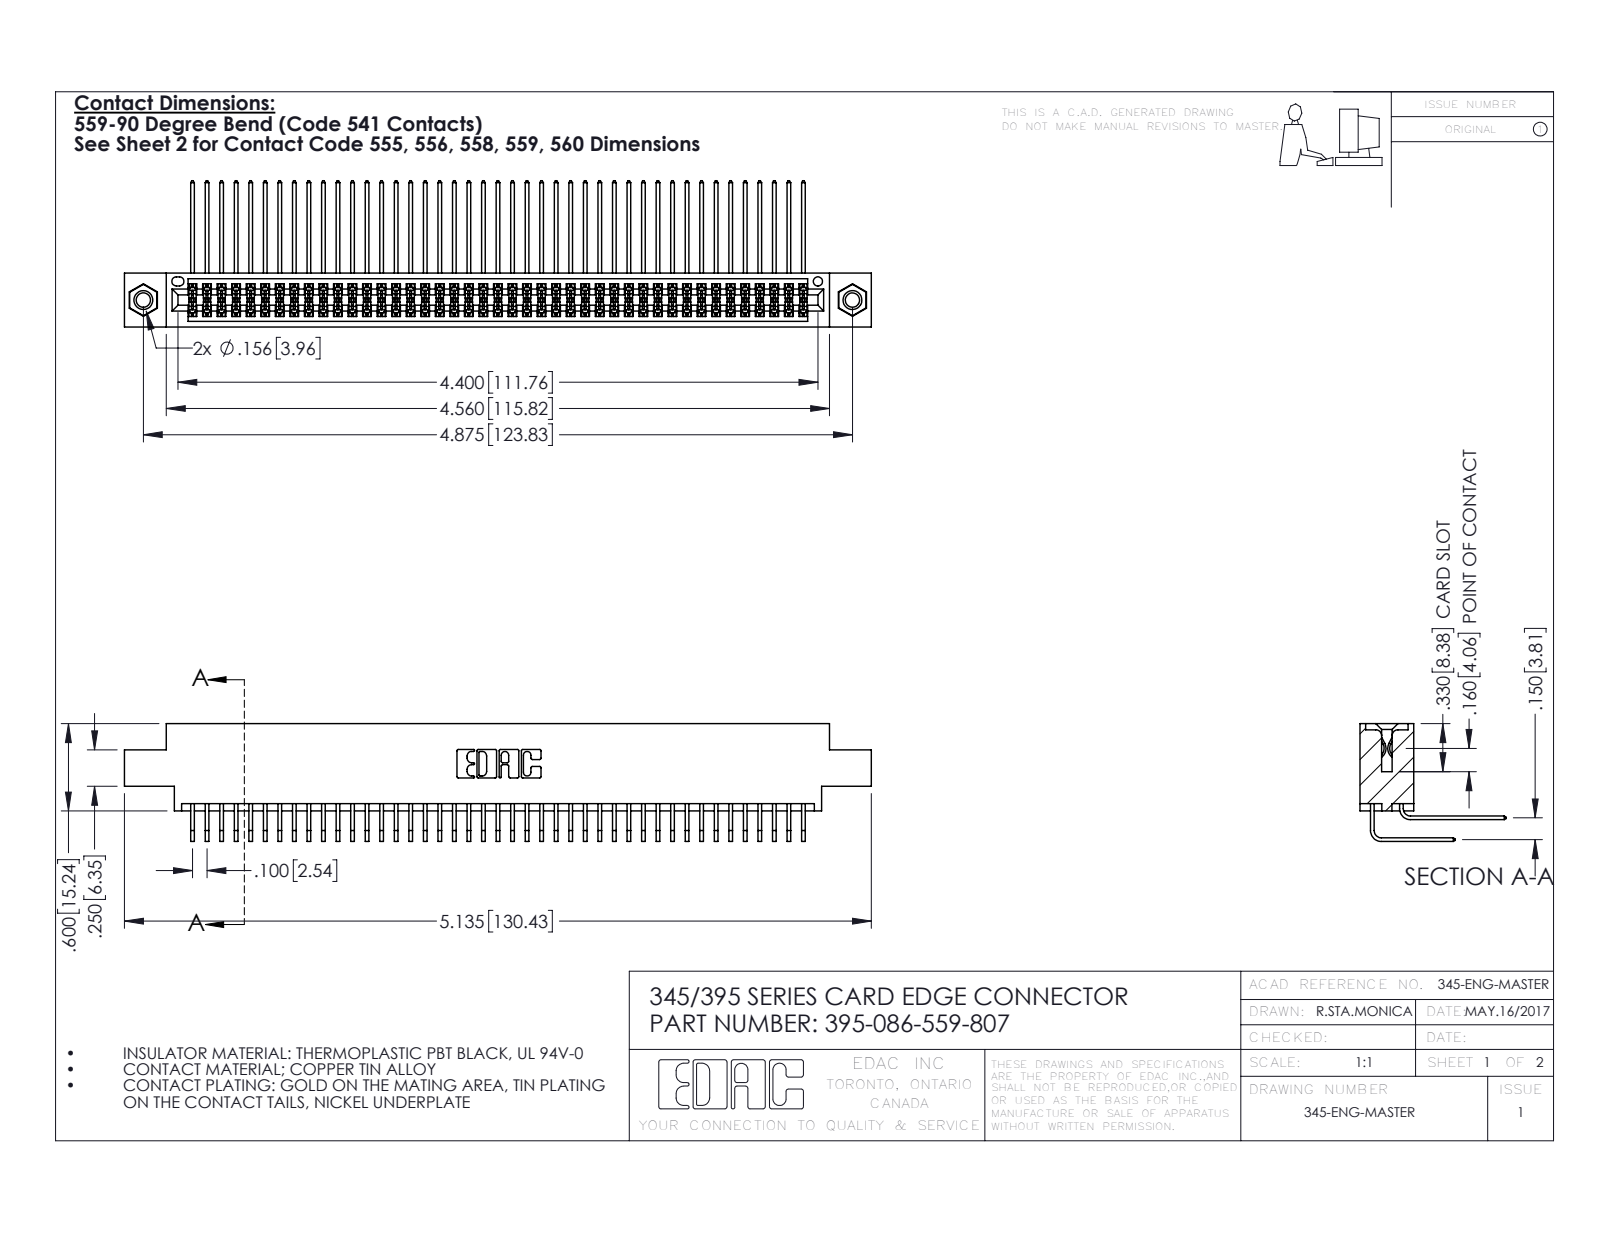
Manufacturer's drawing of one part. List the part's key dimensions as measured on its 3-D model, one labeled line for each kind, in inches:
Part name (STEP PRODUCT): 395-086-559-807; 345-292-001_558 559 Tail - 1; 345 Part_0.170 Offset - 0.156 Dia-TI; 345-292-001_559 Tail - 2 (+1 more)
STEP written by: SolidWorks 2016 (CONFIG_CONTROL_DESIGN)
Units: inches
Bodies: 89 solids, 4662 faces (3126 planar, 1520 cylindrical, 16 other)
Overall size (bounding box): 5.135 × 1.005 × 0.809
Volume: 0.796 in³ · Surface area: 33.81 in²
Round holes (diameter × count): ⌀0.098 ×2, ⌀0.125 ×2, ⌀0.156 ×2, ⌀0.064 ×1
Round bosses / shafts (diameter × count): ⌀0.155 ×2
Partial cylindrical surfaces — rounded edges, fillets, slot ends (radius × count): R0.006 ×130, R0.01 ×22, R0.007 ×6, R0.031 ×6, R0.026 ×3, R0.014 ×2, R0.019 ×2, R0.022 ×2
Main face-to-face distances: 0.072, 0.298, 0.37, 0.2, 0.098, 0.272, 0.025, 0.225, 0.175, 0.15
Hole centre spacings: 0.27, 4.639, 4.875
